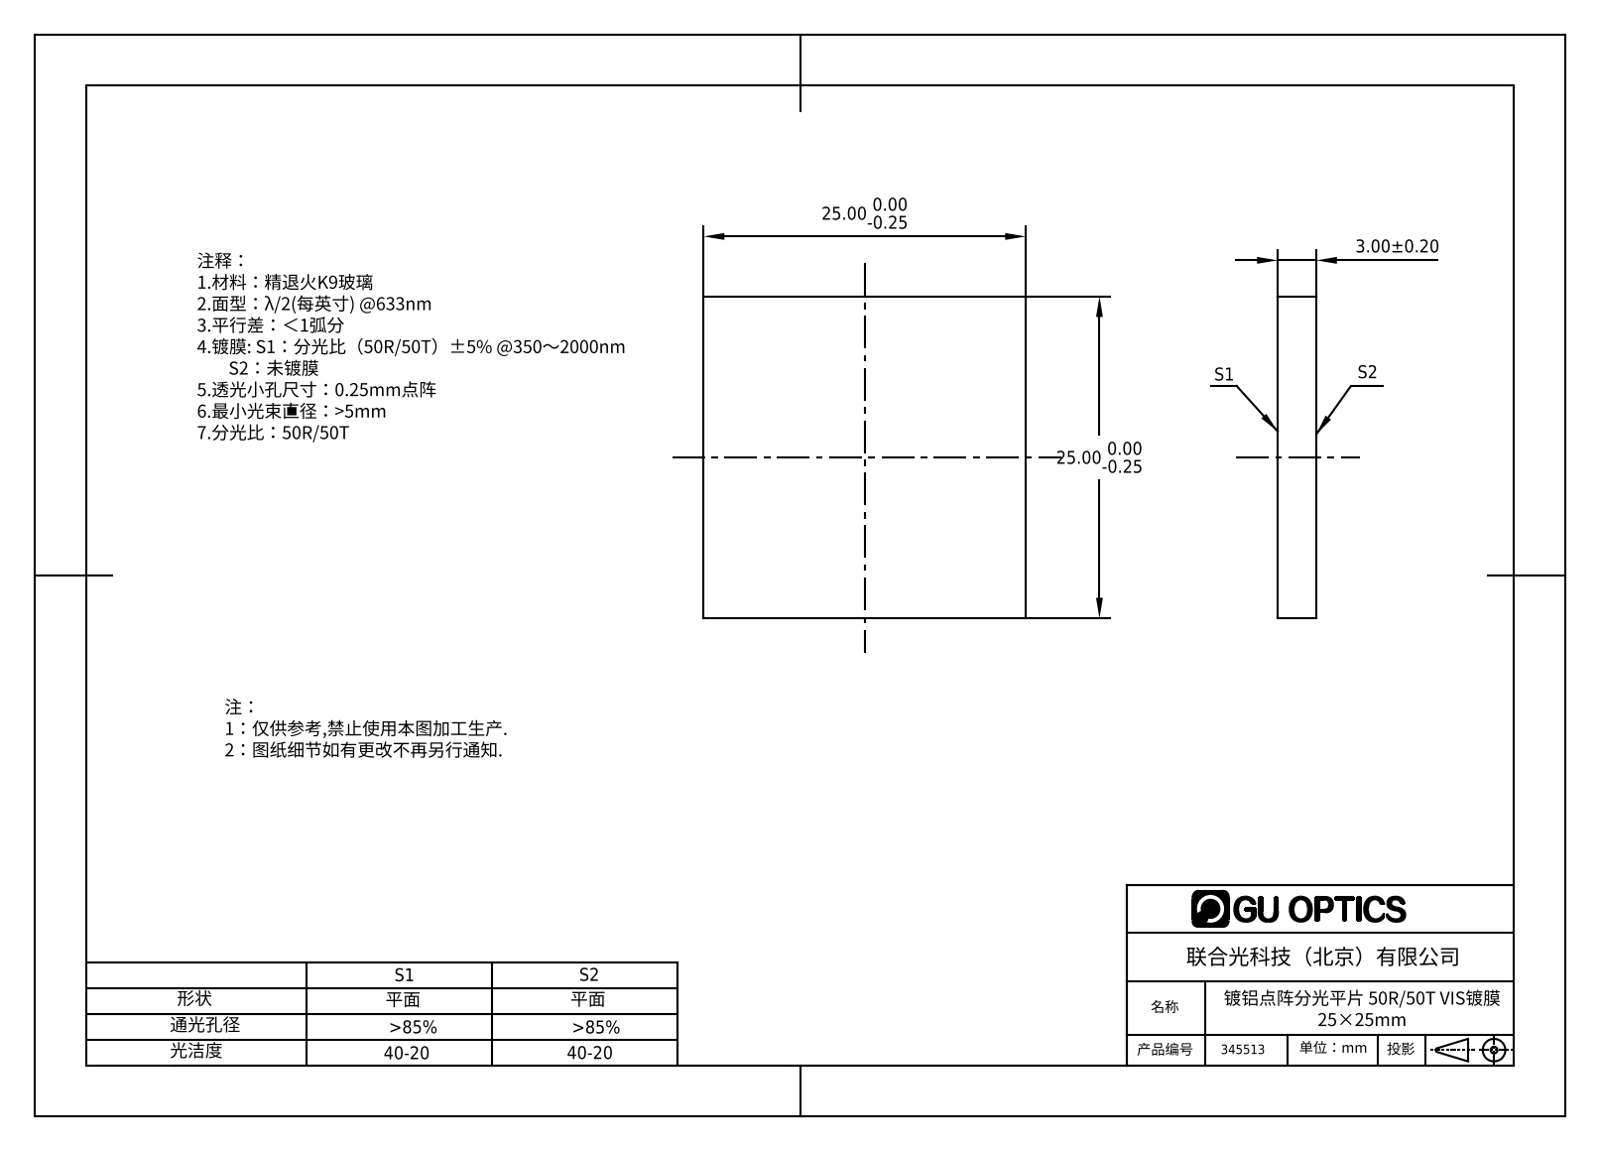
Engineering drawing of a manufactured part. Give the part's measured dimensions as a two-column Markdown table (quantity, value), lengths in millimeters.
| quantity | value |
| --- | --- |
| part name | 345504 |
| STEP written by | SolidWorks 2016 (AUTOMOTIVE_DESIGN) |
| units | millimeters |
| bodies | 1 solid, 6 faces (6 planar, 0 cylindrical, 0 other) |
| overall size | 25 × 25 × 3 |
| volume | 1 875 mm³ |
| surface area | 1 550 mm² |
| main face-to-face distances | 3, 25 |
